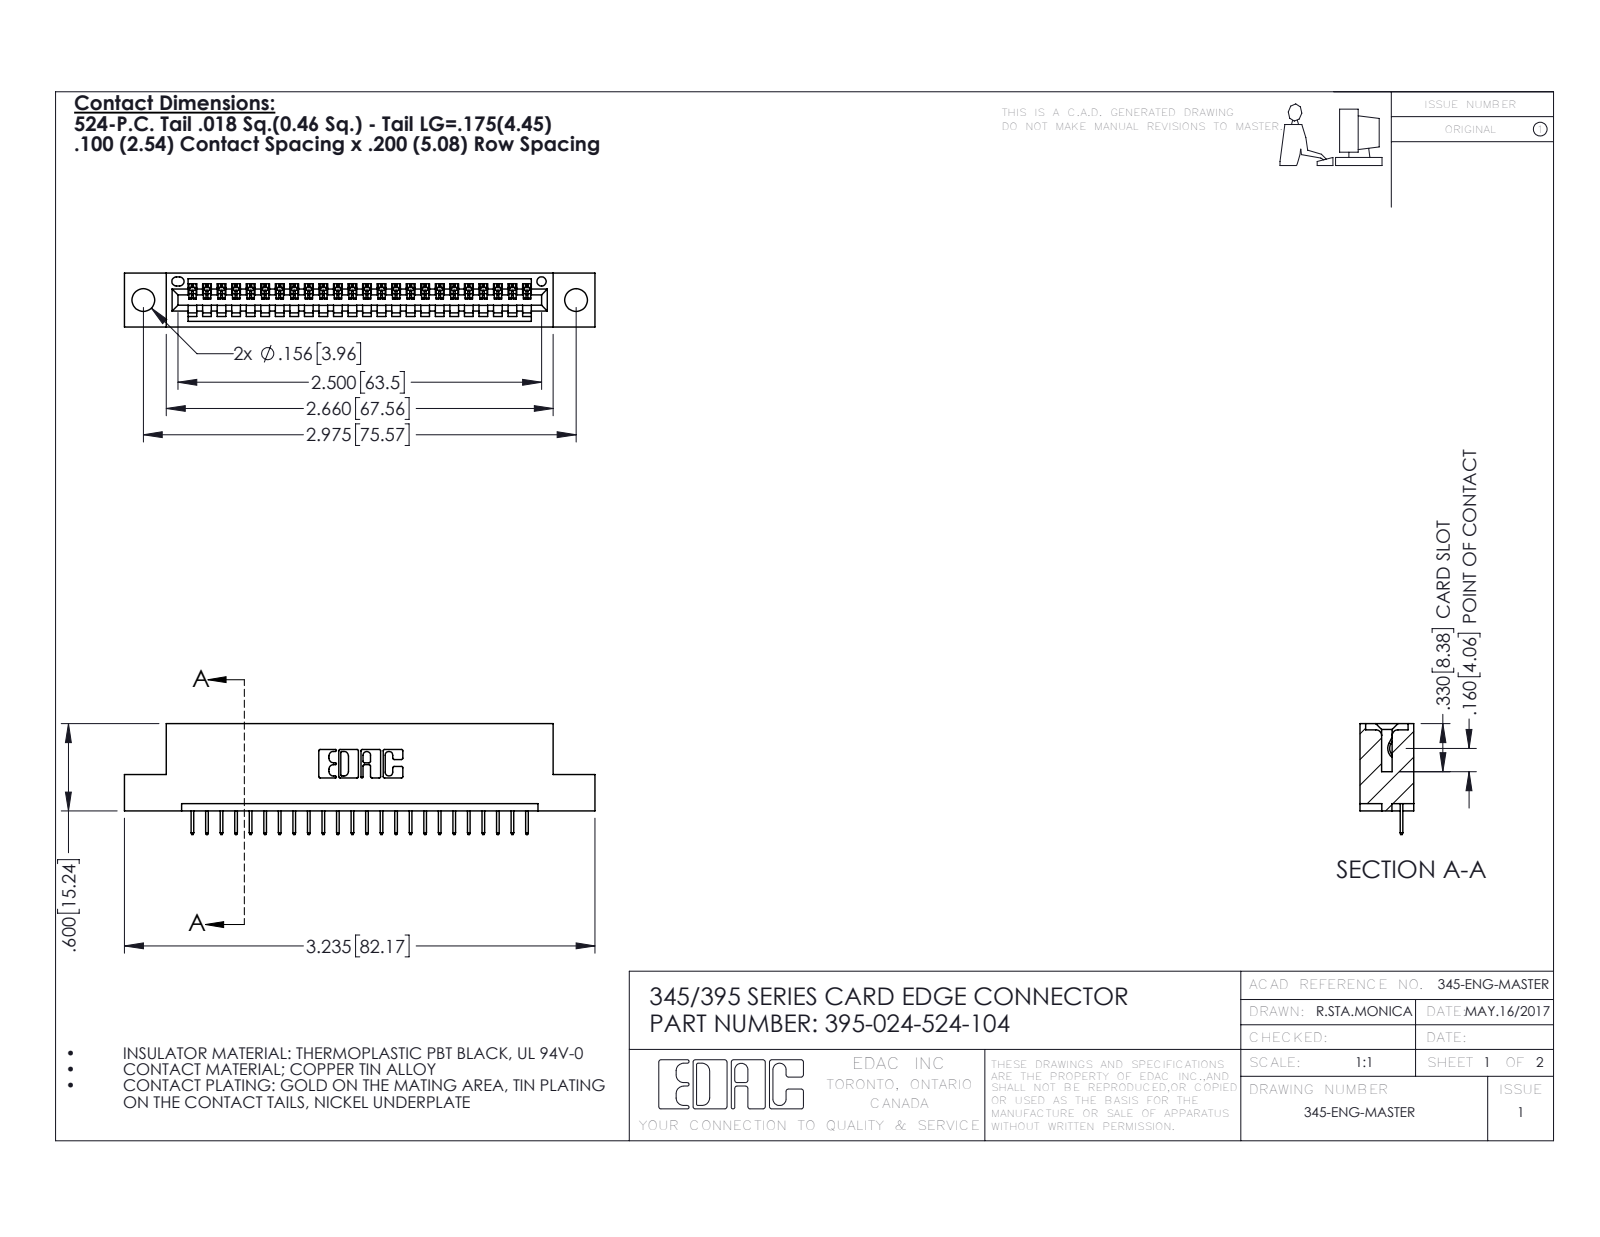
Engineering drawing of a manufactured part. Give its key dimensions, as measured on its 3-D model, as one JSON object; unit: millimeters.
{"part_name": "345 Part_Flush Mounting Lugs - 0.156 Dia-TH; 345-292-001_345-293-124; 395-024-524-104", "step_written_by": "SolidWorks 2016 (CONFIG_CONTROL_DESIGN)", "units": "millimeters", "bodies": {"solids": 25, "faces": 1614, "planar": 1184, "cylindrical": 430, "other": 0}, "overall_size": [82.2, 19.4, 9.4], "volume_mm3": 7470, "surface_area_mm2": 9194, "round_holes": [[4, 2], [1.6, 1]], "partial_cylinders_radius": [[0.2, 48], [0.3, 22], [0.2, 6], [0.8, 6], [0.7, 3], [0.8, 2], [1, 2], [0.4, 1]], "face_to_face_distances": [7.6, 1.8, 9.4, 5.1, 2.5, 6.9, 0.6, 5.7, 1.8, 3.8], "hole_center_spacings": [6.9, 69.6, 75.6]}
